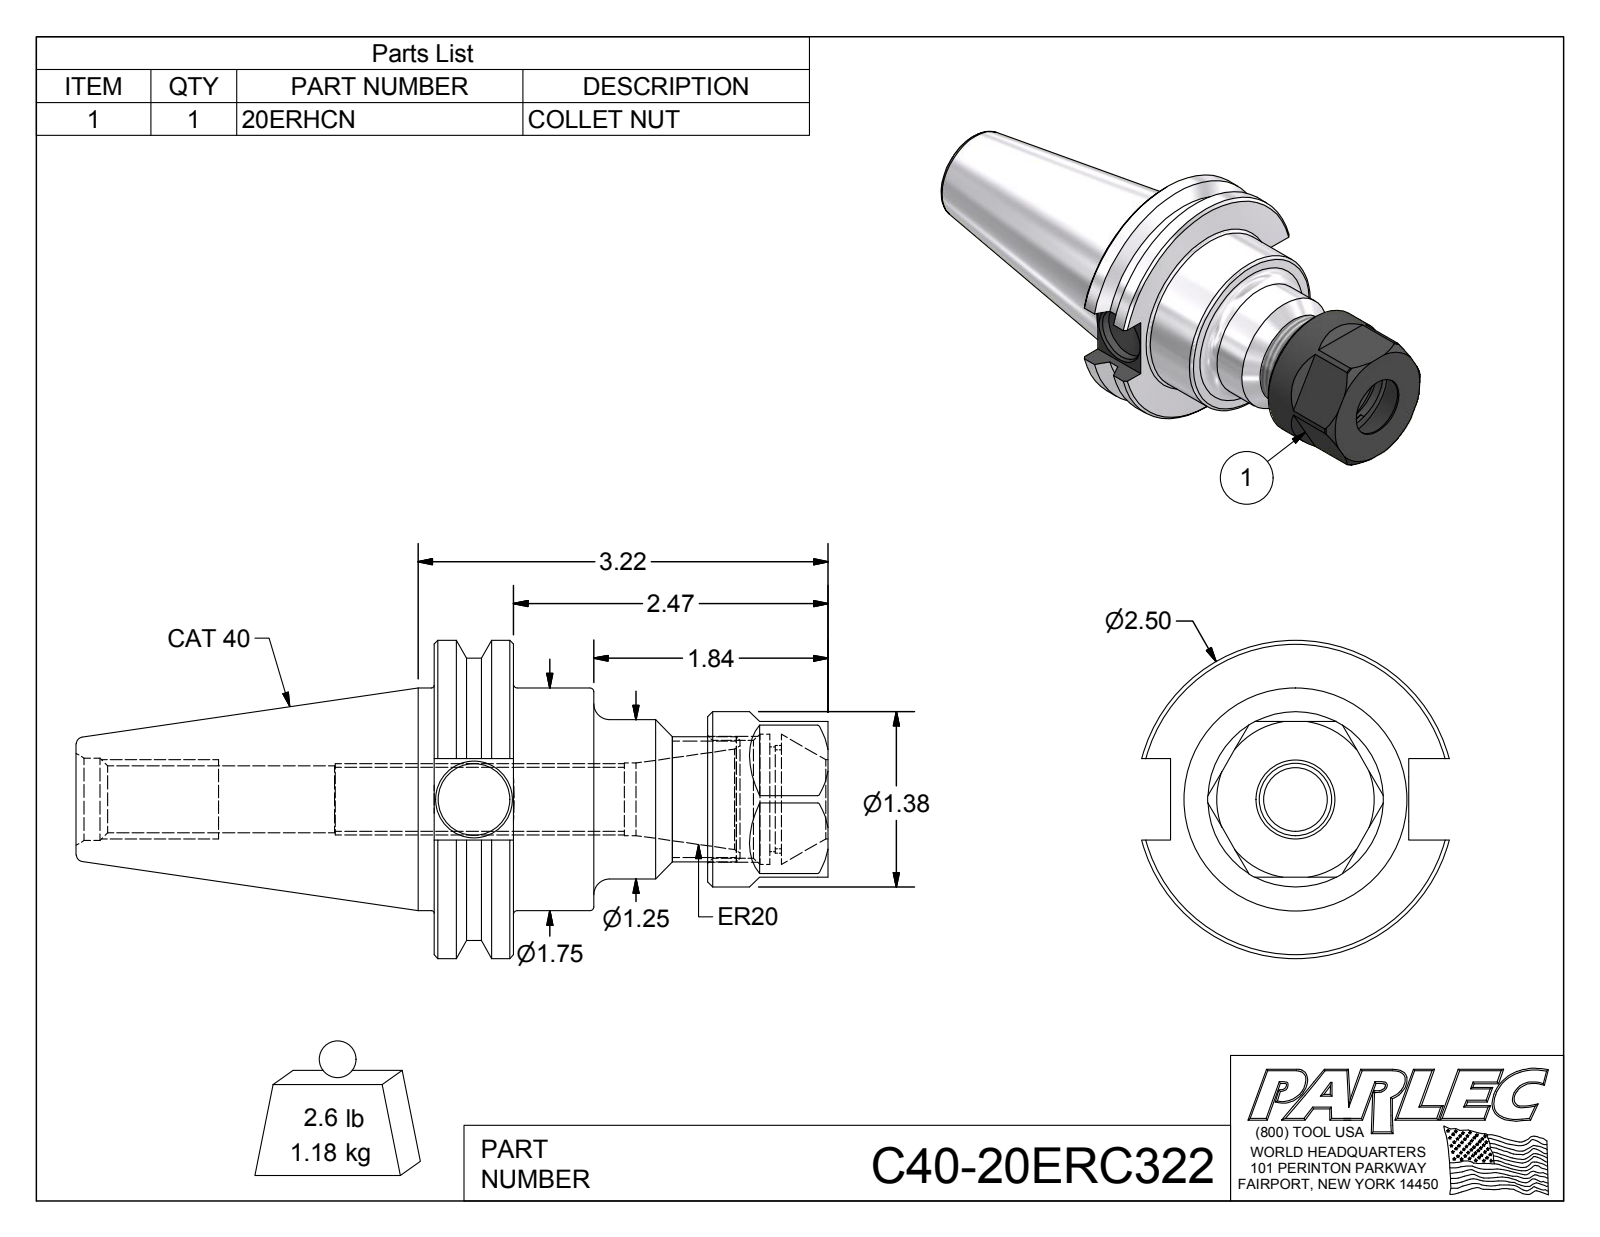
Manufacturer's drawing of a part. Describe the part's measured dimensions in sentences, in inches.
The part is named "C40-20ER3-1; 20ERHCN; C40-20ERC322". Its 3-D file was written by "Autodesk Inventor 2016 (AUTOMOTIVE_DESIGN)". It is 2 solids with 91 faces: 30 planar, 22 cylindrical and 39 other. Overall it measures 5.907 by 2.5 by 2.417 inches. Its volume is 9.021 cubic inches and its surface area 50.03 square inches. Round holes: 1 of diameter 0.315, 1 of diameter 0.399, 1 of diameter 0.502, 1 of diameter 0.527, 1 of diameter 0.57, 1 of diameter 0.62, 1 of diameter 0.648, 1 of diameter 0.82, 1 of diameter 0.925, 1 of diameter 1.024. Round bosses or shafts: 1 of diameter 2.5, 1 of diameter 2.219, 1 of diameter 1.75, 1 of diameter 1.378, 1 of diameter 1.25, 1 of diameter 0.984. Partial cylindrical surfaces (rounded edges, fillets, slot ends): 1 of radius 0.423. The main face-to-face distances are 0.625, 1.22, 3.095, 2.47, 0.29, 0.93, 2.15, 1.525, 0.945, 1.255. The hole center spacings are 0.037.
